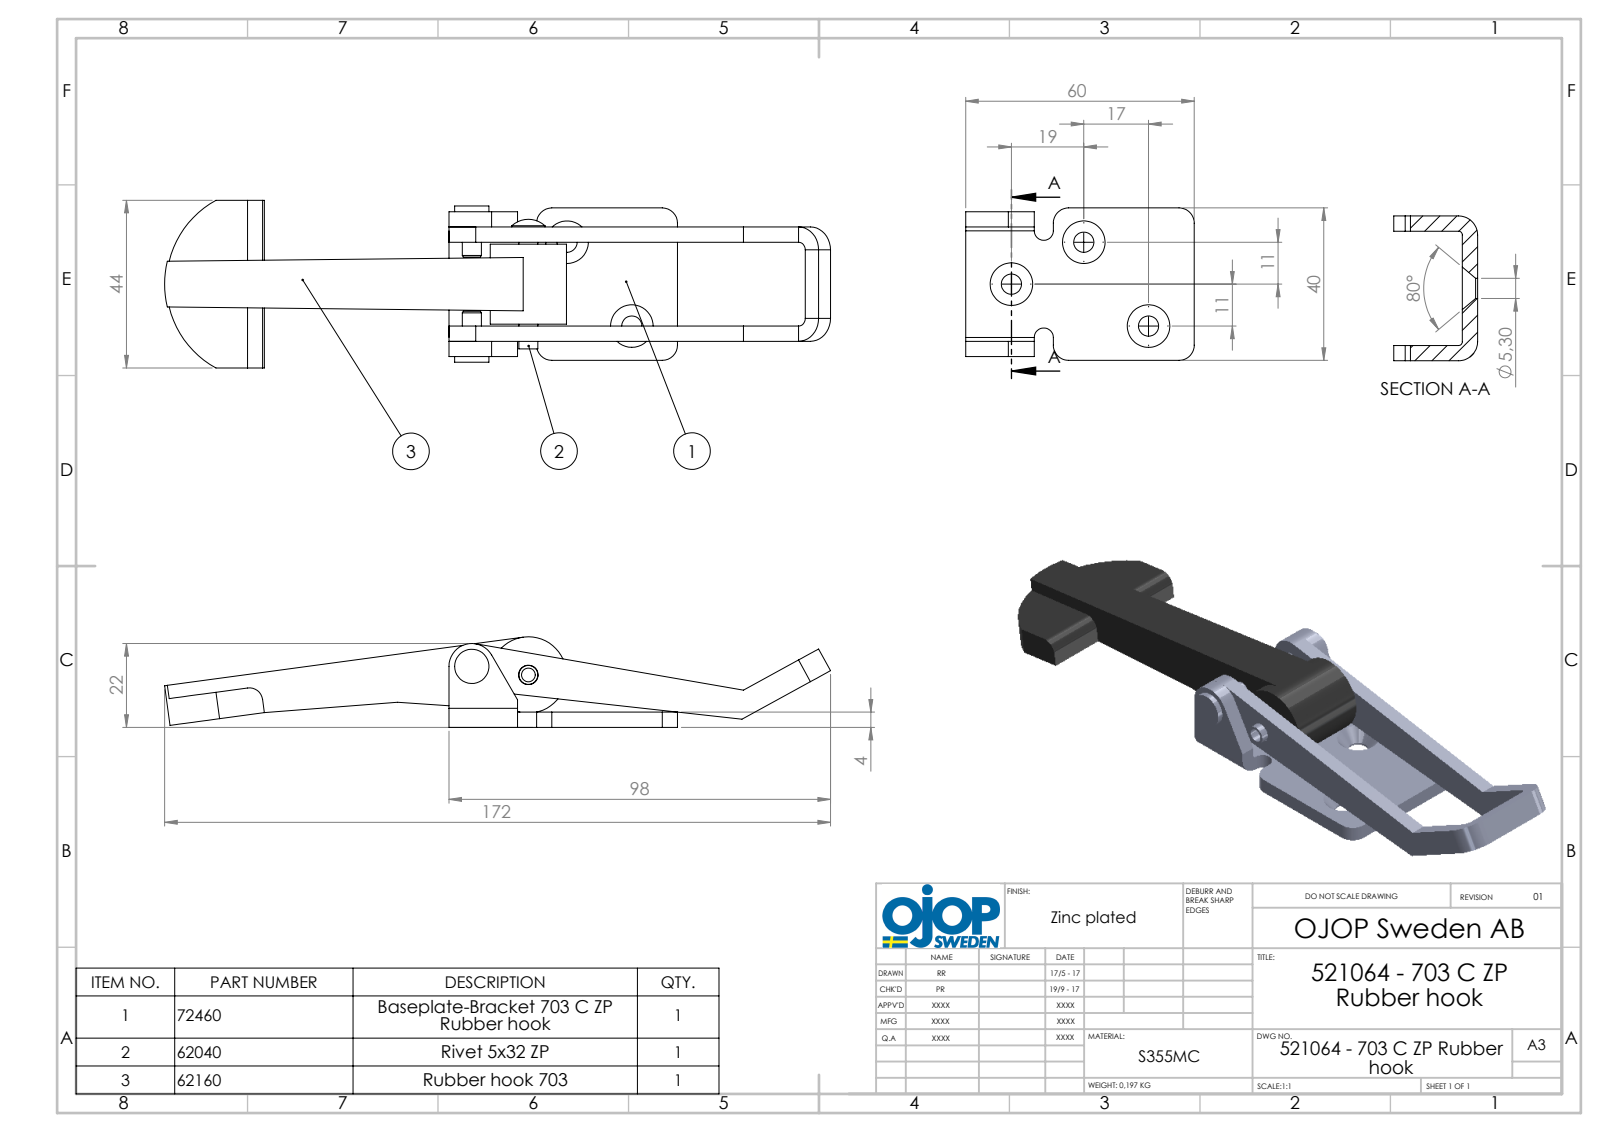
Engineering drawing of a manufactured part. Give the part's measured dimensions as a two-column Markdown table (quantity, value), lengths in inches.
| quantity | value |
| --- | --- |
| part name | gummihake 703; 521064 - 703 C ZP Rubber hook; nit703; 703 - Bygel (+2 more) |
| STEP written by | SolidWorks 2015 (AUTOMOTIVE_DESIGN) |
| units | inches |
| bodies | 6 solids, 139 faces (67 planar, 60 cylindrical, 12 other) |
| overall size | 6.882 × 1.732 × 0.935 |
| volume | 2.634 in³ |
| surface area | 34.34 in² |
| round holes (diameter × count) | 0.209 × 3, 0.201 × 2, 0.098 × 1, 0.217 × 1, 0.283 × 1 |
| round bosses / shafts (diameter × count) | 0.197 × 2, 0.787 × 1, 0.354 × 1, 0.276 × 1 |
| partial cylindrical surfaces (radius × count) | 0.157 × 4, 0.236 × 3, 0.039 × 2, 0.079 × 2, 0.098 × 2, 0.197 × 2, 0.138 × 1, 0.984 × 1 |
| main face-to-face distances | 0.157, 1.024, 1.181, 0.413, 0.866, 0.02, 0.177, 1.004, 0.846, 0.139 |
| hole center spacings | 0.591, 0.864, 1.094, 1.482 |
